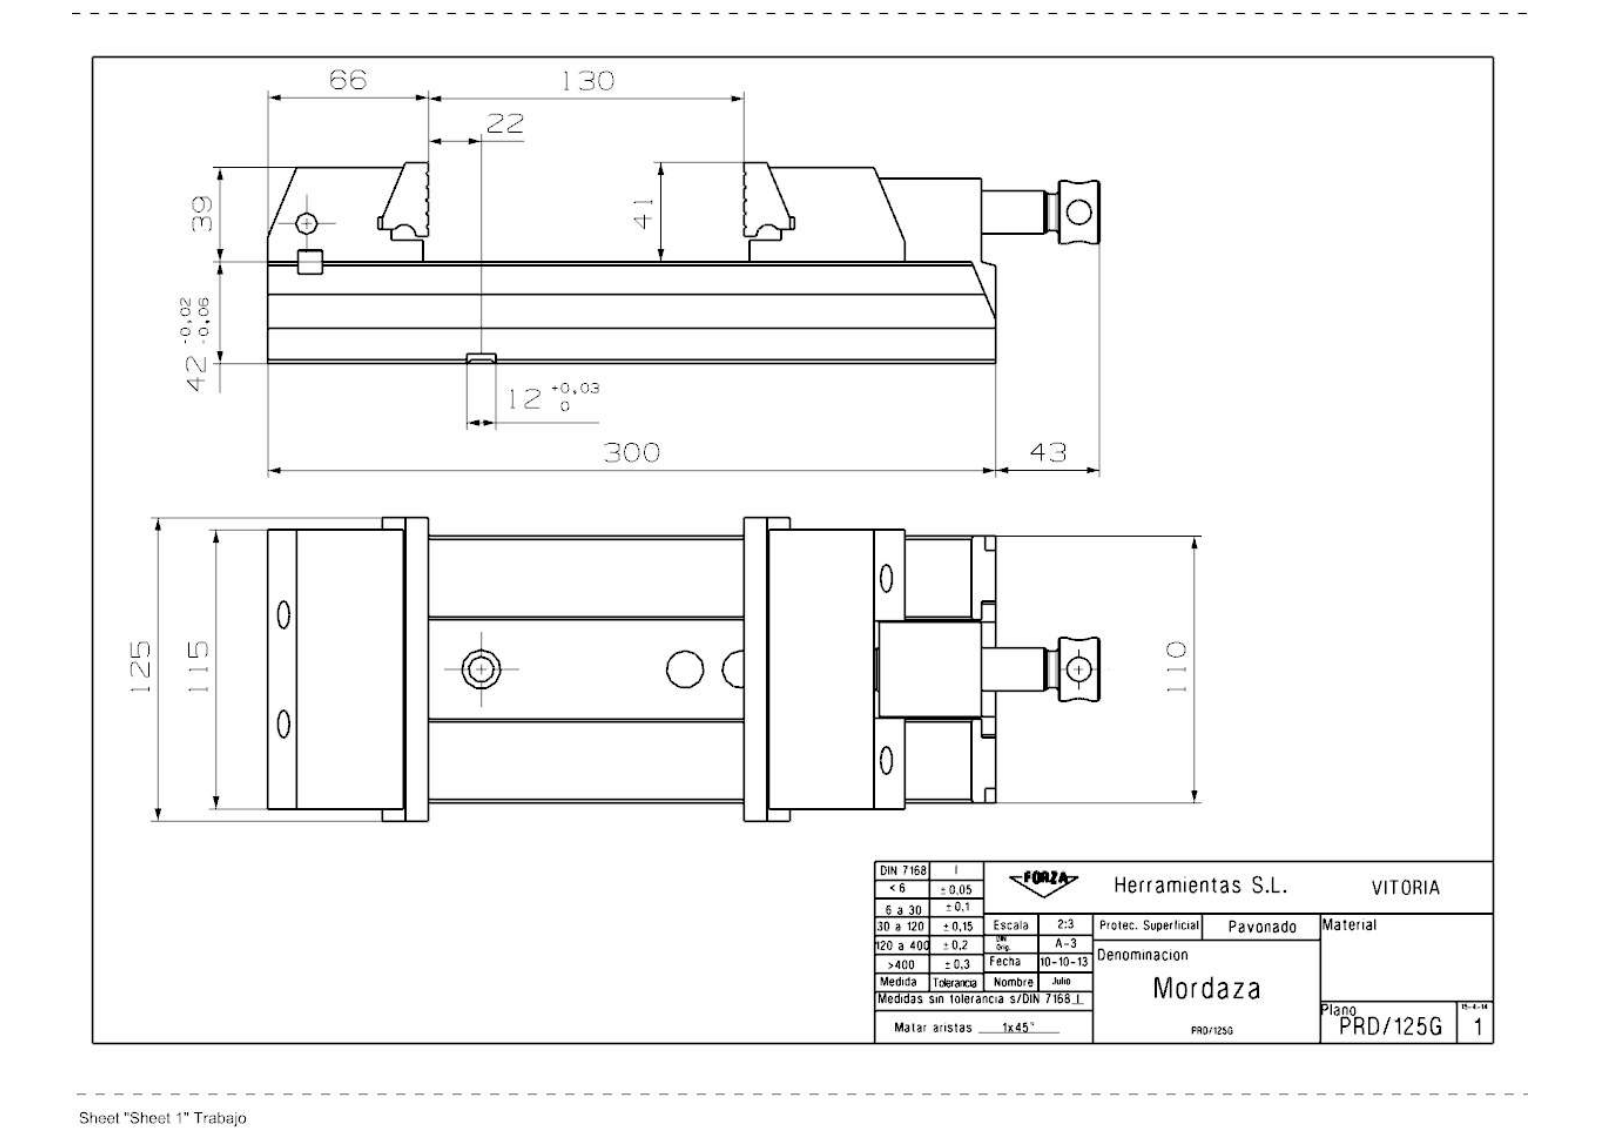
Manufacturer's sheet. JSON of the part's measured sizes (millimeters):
{"part_name": "30_125G_Mordaza", "step_written_by": "SIEMENS PLM Software NX 7.5 (AUTOMOTIVE_DESIGN)", "units": "millimeters", "bodies": {"solids": 11, "faces": 455, "planar": 290, "cylindrical": 122, "other": 43}, "overall_size": [355.83, 125, 83], "volume_mm3": 1572000, "surface_area_mm2": 275407, "round_holes": [[4.35, 5], [5.19, 4], [6.5, 4], [7.5, 4], [11.5, 4], [8.78, 3], [6.99, 2], [8, 2], [10, 2], [10.5, 2], [11, 2], [12.38, 2]], "round_bosses_or_shafts": [[26, 1], [17.73, 1], [15, 1], [14.5, 1], [10.5, 1]], "partial_cylinders_radius": [[0.3, 20], [6, 7], [10, 4], [16, 4], [1.6, 2], [5, 2], [3, 1], [8, 1]], "face_to_face_distances": [42, 8.5, 15.4, 26.6, 6, 39, 77, 29.5, 27, 81], "hole_center_spacings": [60, 75, 0.7, 8.95, 9.19, 15, 15.02, 23.16]}
